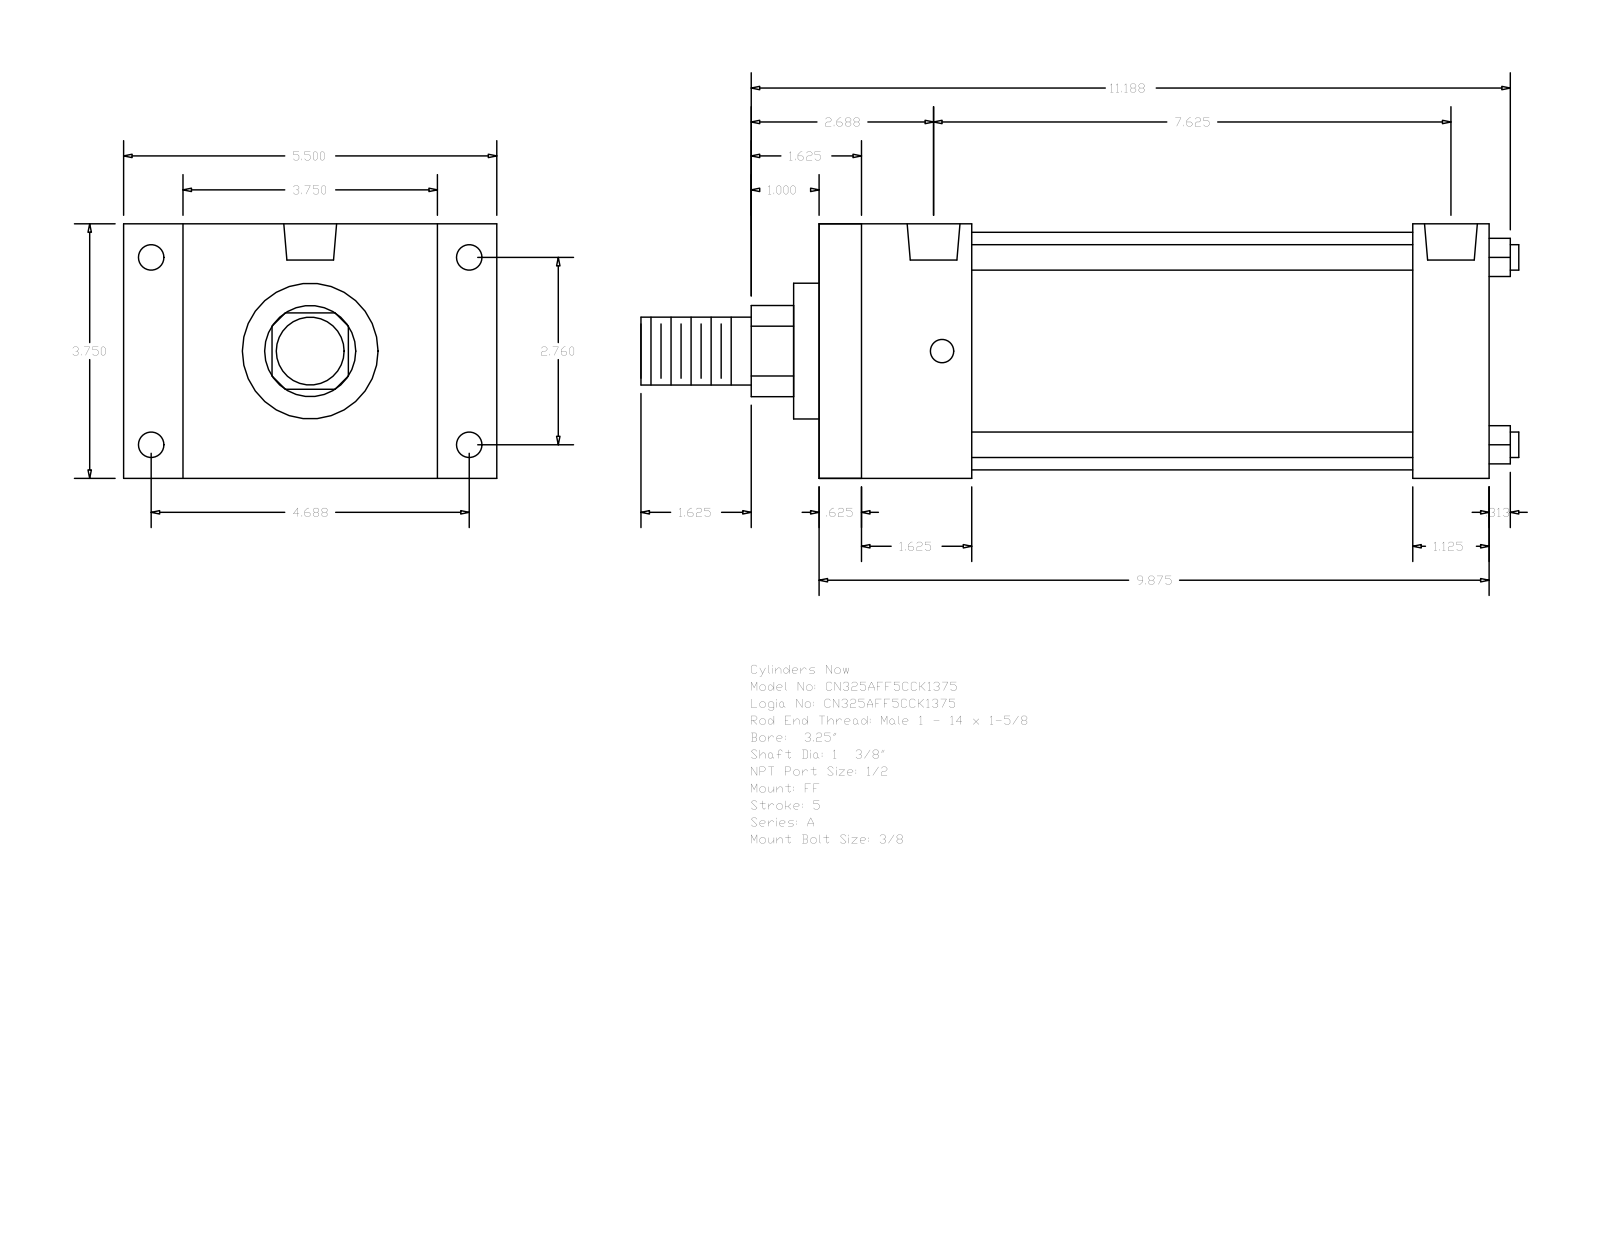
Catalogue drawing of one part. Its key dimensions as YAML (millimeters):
part_name: "A_FF__0325_1.375"
step_written_by: "GSSL Pune (CONFIG_CONTROL_DESIGN)"
units: millimeters
bodies: {solids: 0, faces: 92, planar: 64, cylindrical: 28, other: 0}
overall_size: [328.61, 139.7, 95.25]
round_holes:
  - {diameter: 8.73, count: 4}
  - {diameter: 9.53, count: 4}
  - {diameter: 19.77, count: 2}
round_bosses_or_shafts:
  - {diameter: 9.53, count: 4}
  - {diameter: 88.9, count: 1}
  - {diameter: 50.8, count: 1}
  - {diameter: 34.92, count: 1}
  - {diameter: 25.4, count: 1}
partial_cylinders:
  - {radius: 17.06, count: 1}
face_to_face_distances: [95.24, 250.83, 15.87, 234.96, 57.15, 28.58, 22.23, 117.47, 222.25, 41.28]
hole_center_spacings: [3.18, 70.1, 119.06, 138.16, 187.32, 190.5, 193.68]
